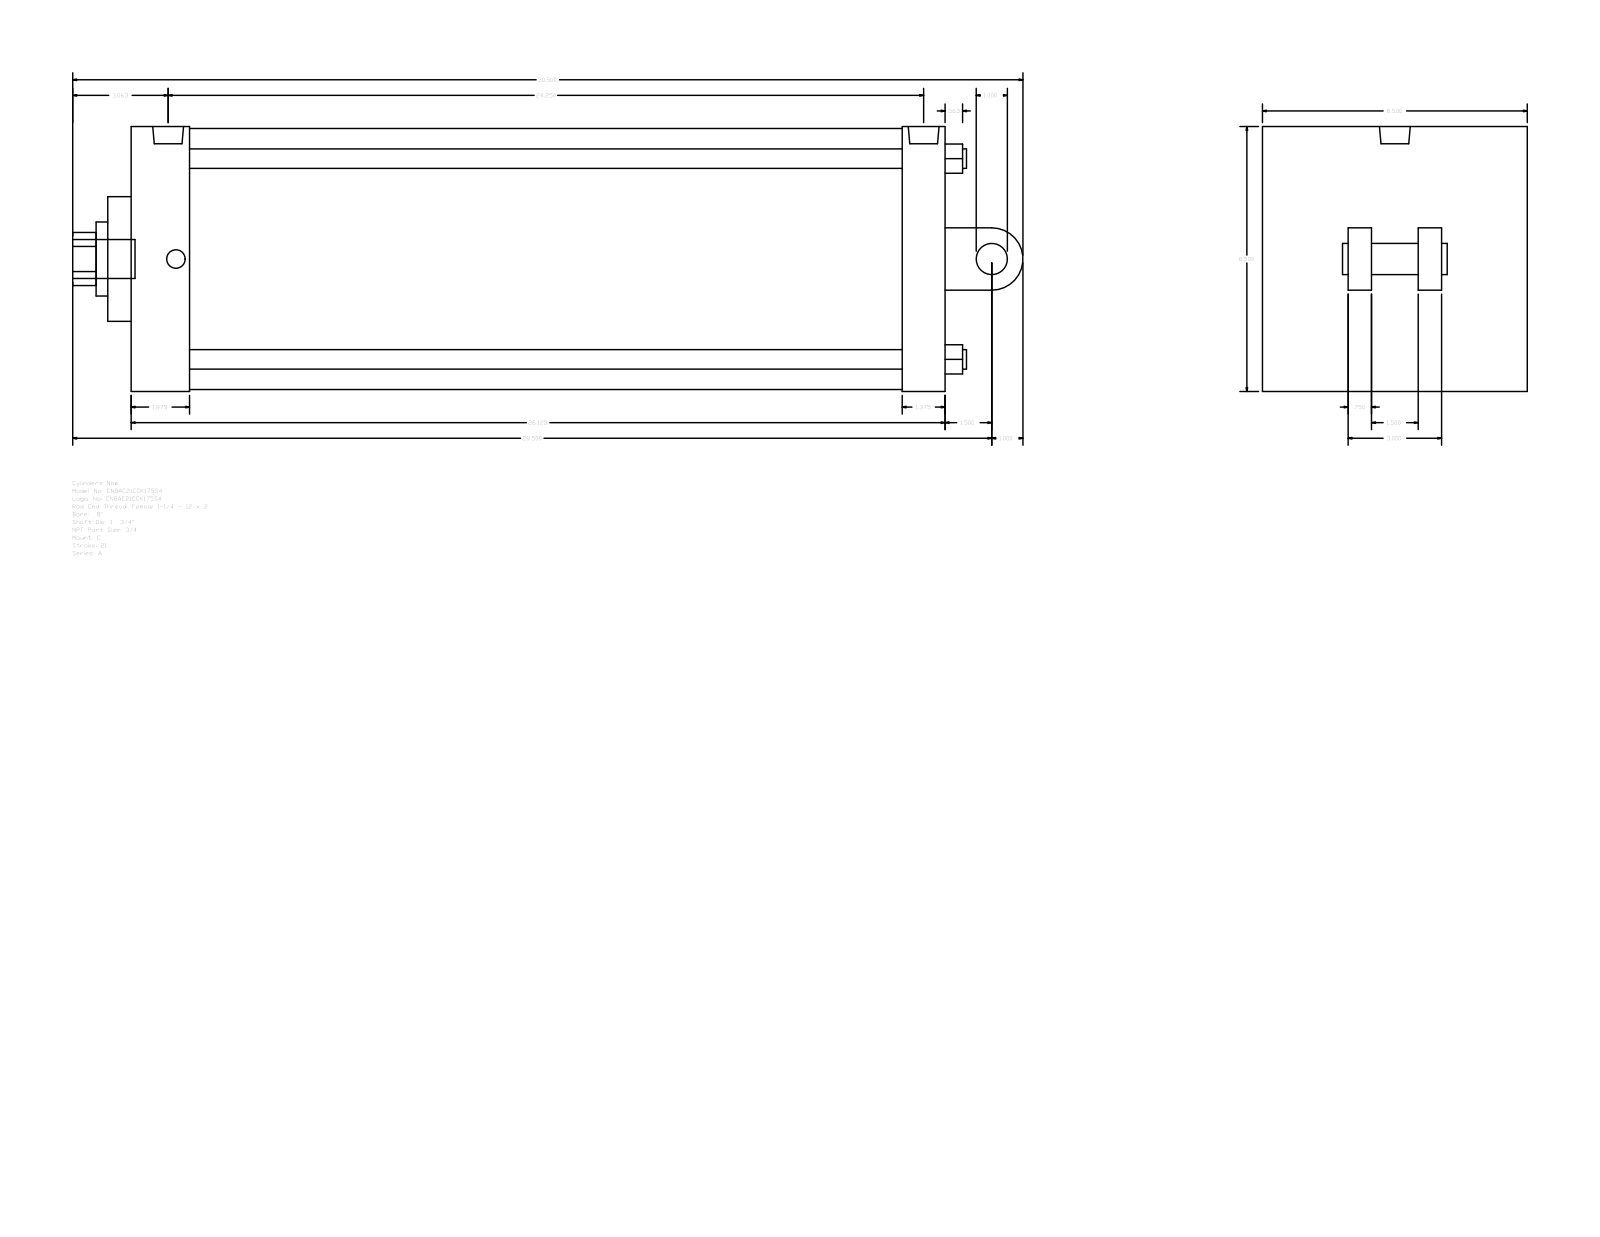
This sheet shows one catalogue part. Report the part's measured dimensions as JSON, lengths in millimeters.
{"part_name": "A_C__0800_1.75", "step_written_by": "GSSL Pune (CONFIG_CONTROL_DESIGN)", "units": "millimeters", "bodies": {"solids": 0, "faces": 104, "planar": 75, "cylindrical": 29, "other": 0}, "overall_size": [774.7, 215.9, 215.9], "round_holes": [[15.88, 4], [15.08, 2], [25.12, 1], [44.45, 1], [60.33, 1], [212.72, 1]], "round_bosses_or_shafts": [[15.08, 2], [31.75, 1], [25.4, 1], [25.12, 1]], "partial_cylinders_radius": [[21.63, 1], [25.4, 1]], "face_to_face_distances": [663.58, 215.9, 19.05, 57.15, 47.63, 615.95, 628.65, 581.02, 34.93, 88.9], "hole_center_spacings": [115.67, 163.58, 231.34, 6.35]}
